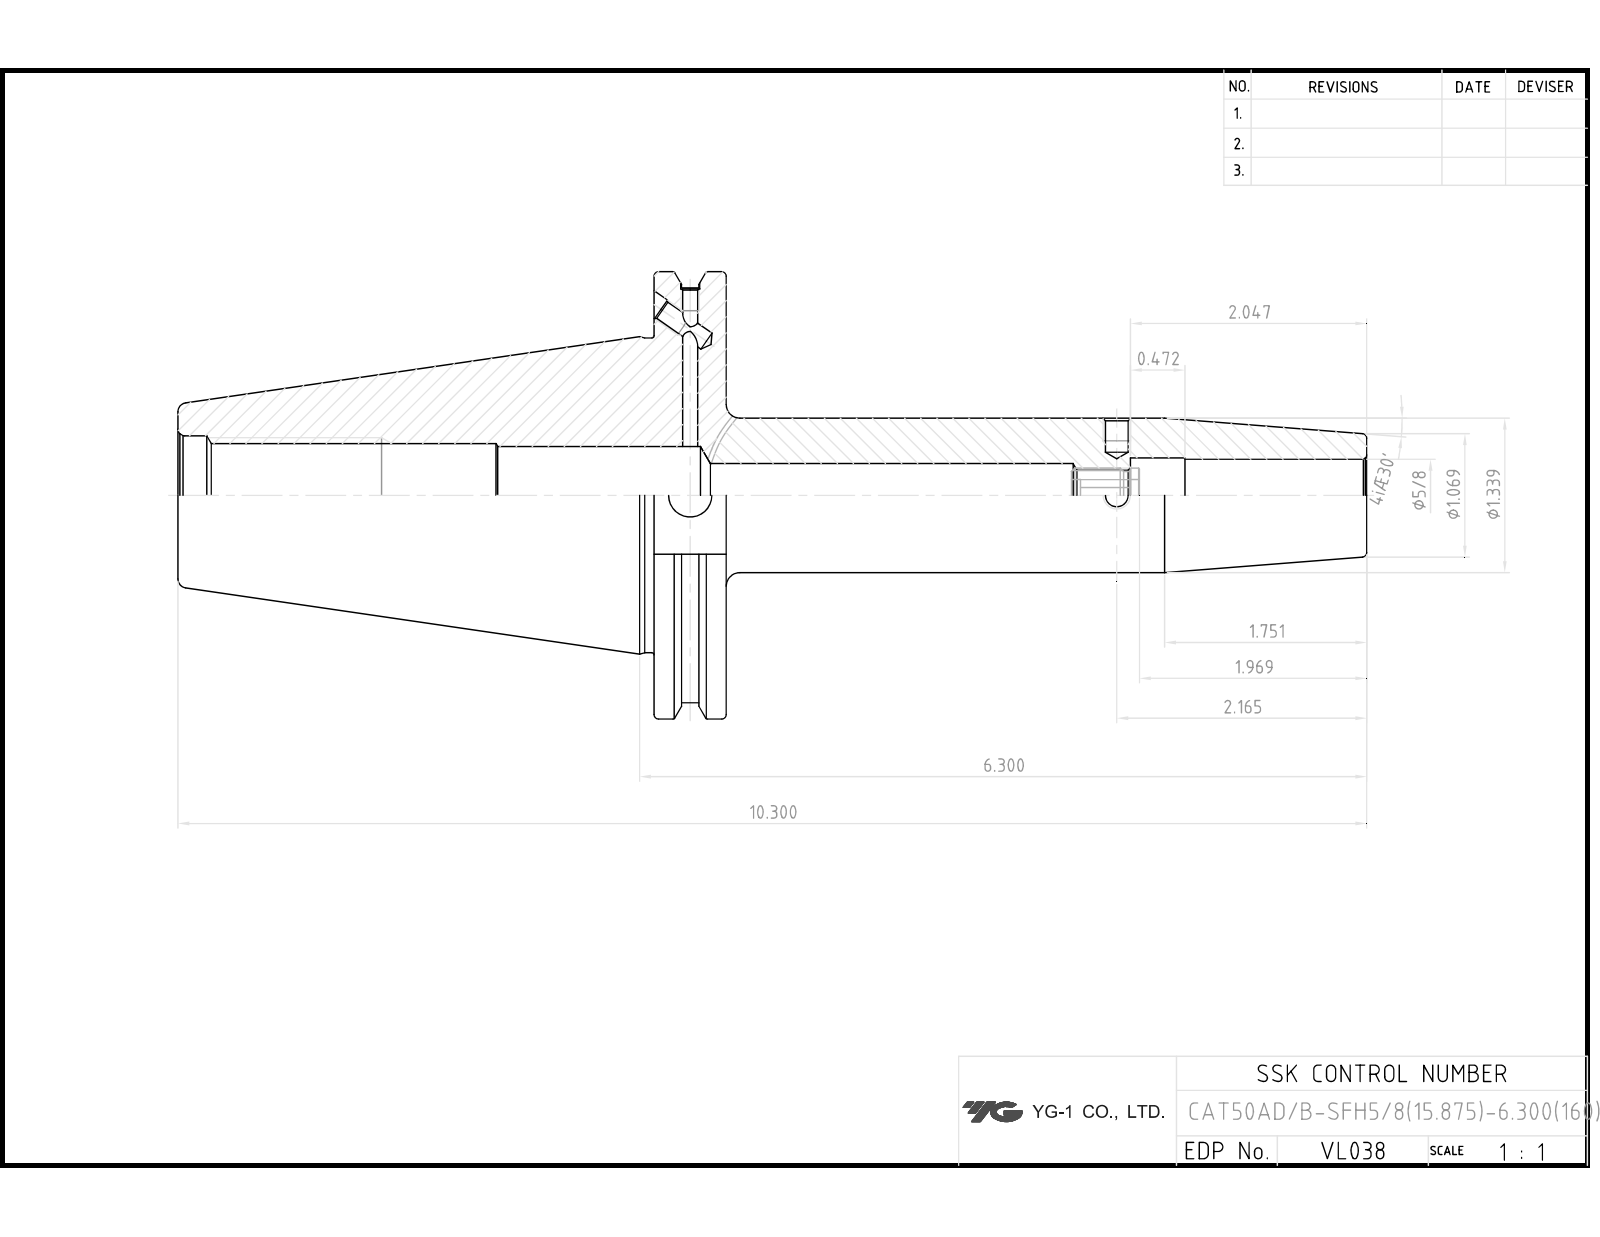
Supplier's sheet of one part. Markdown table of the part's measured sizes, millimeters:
| quantity | value |
| --- | --- |
| part name | LO-CAT50ADB-SFH15.875-160 |
| STEP written by | Autodesk Inventor 2025 (AUTOMOTIVE_DESIGN) |
| units | millimeters |
| bodies | 1 solid, 86 faces (37 planar, 27 cylindrical, 22 other) |
| overall size | 261.6 × 98.42 × 94.69 |
| volume | 416 703 mm³ |
| surface area | 65 401 mm² |
| round holes (diameter × count) | 3.24 × 2, 4.13 × 2, 4.2 × 2, 5 × 2, 9.53 × 1, 10.92 × 1, 14 × 1, 15.88 × 1, 17.08 × 1, 21.97 × 1, 26.2 × 1 |
| round bosses / shafts (diameter × count) | 98.42 × 1, 91.29 × 1, 69.25 × 1, 34 × 1 |
| main face-to-face distances | 15.88, 104.77, 120.65, 73.03, 25.9, 261.6, 156.83, 140.95, 110.82, 6.05 |
